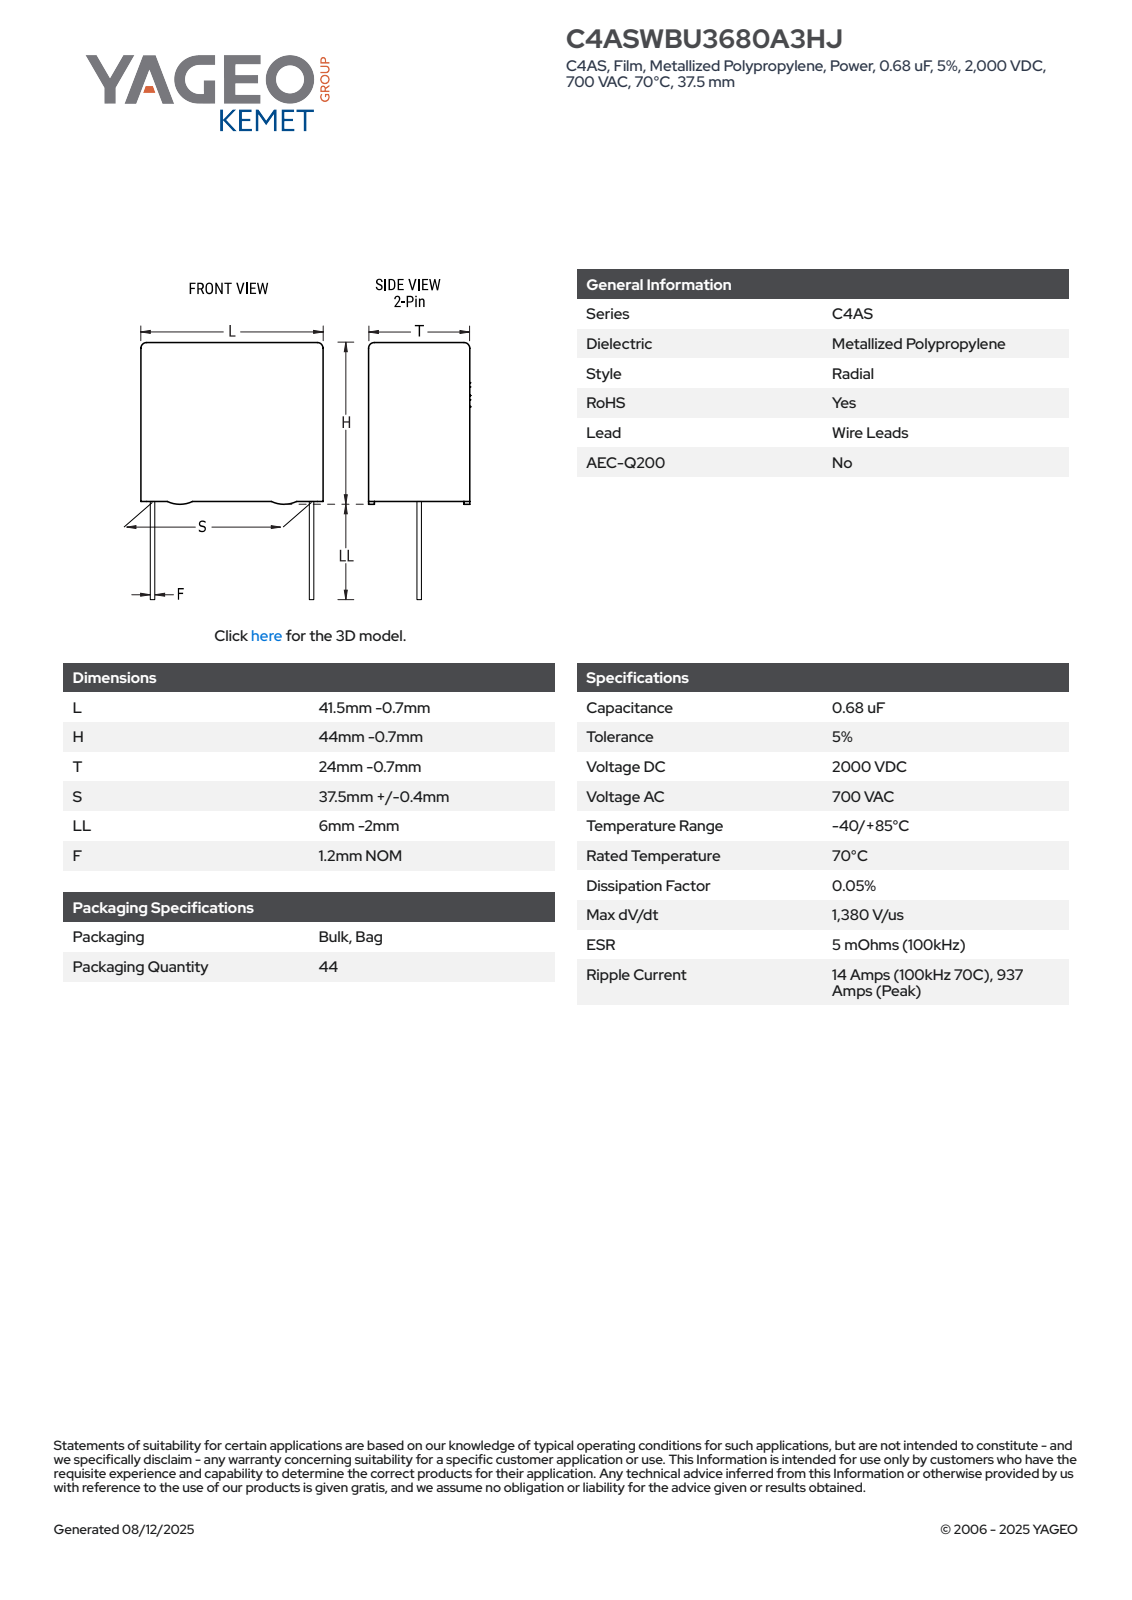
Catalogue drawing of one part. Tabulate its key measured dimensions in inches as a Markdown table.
| quantity | value |
| --- | --- |
| part name | CFP_RB_41.5X44X24_L40.8H43.3T23.3S37.5LL4F1.2 |
| STEP written by | SolidWorks 2014 (AUTOMOTIVE_DESIGN) |
| units | inches |
| bodies | 4 solids, 89 faces (81 planar, 8 cylindrical, 0 other) |
| overall size | 1.862 × 1.606 × 0.917 |
| volume | 2.464 in³ |
| surface area | 11.59 in² |
| round bosses / shafts (diameter × count) | 0.047 × 2 |
| partial cylindrical surfaces (radius × count) | 0.02 × 4 |
| main face-to-face distances | 0.917, 1.606, 1.67, 0.034, 1.705, 0.052, 0.865, 0.918, 0.053, 0.813 |
